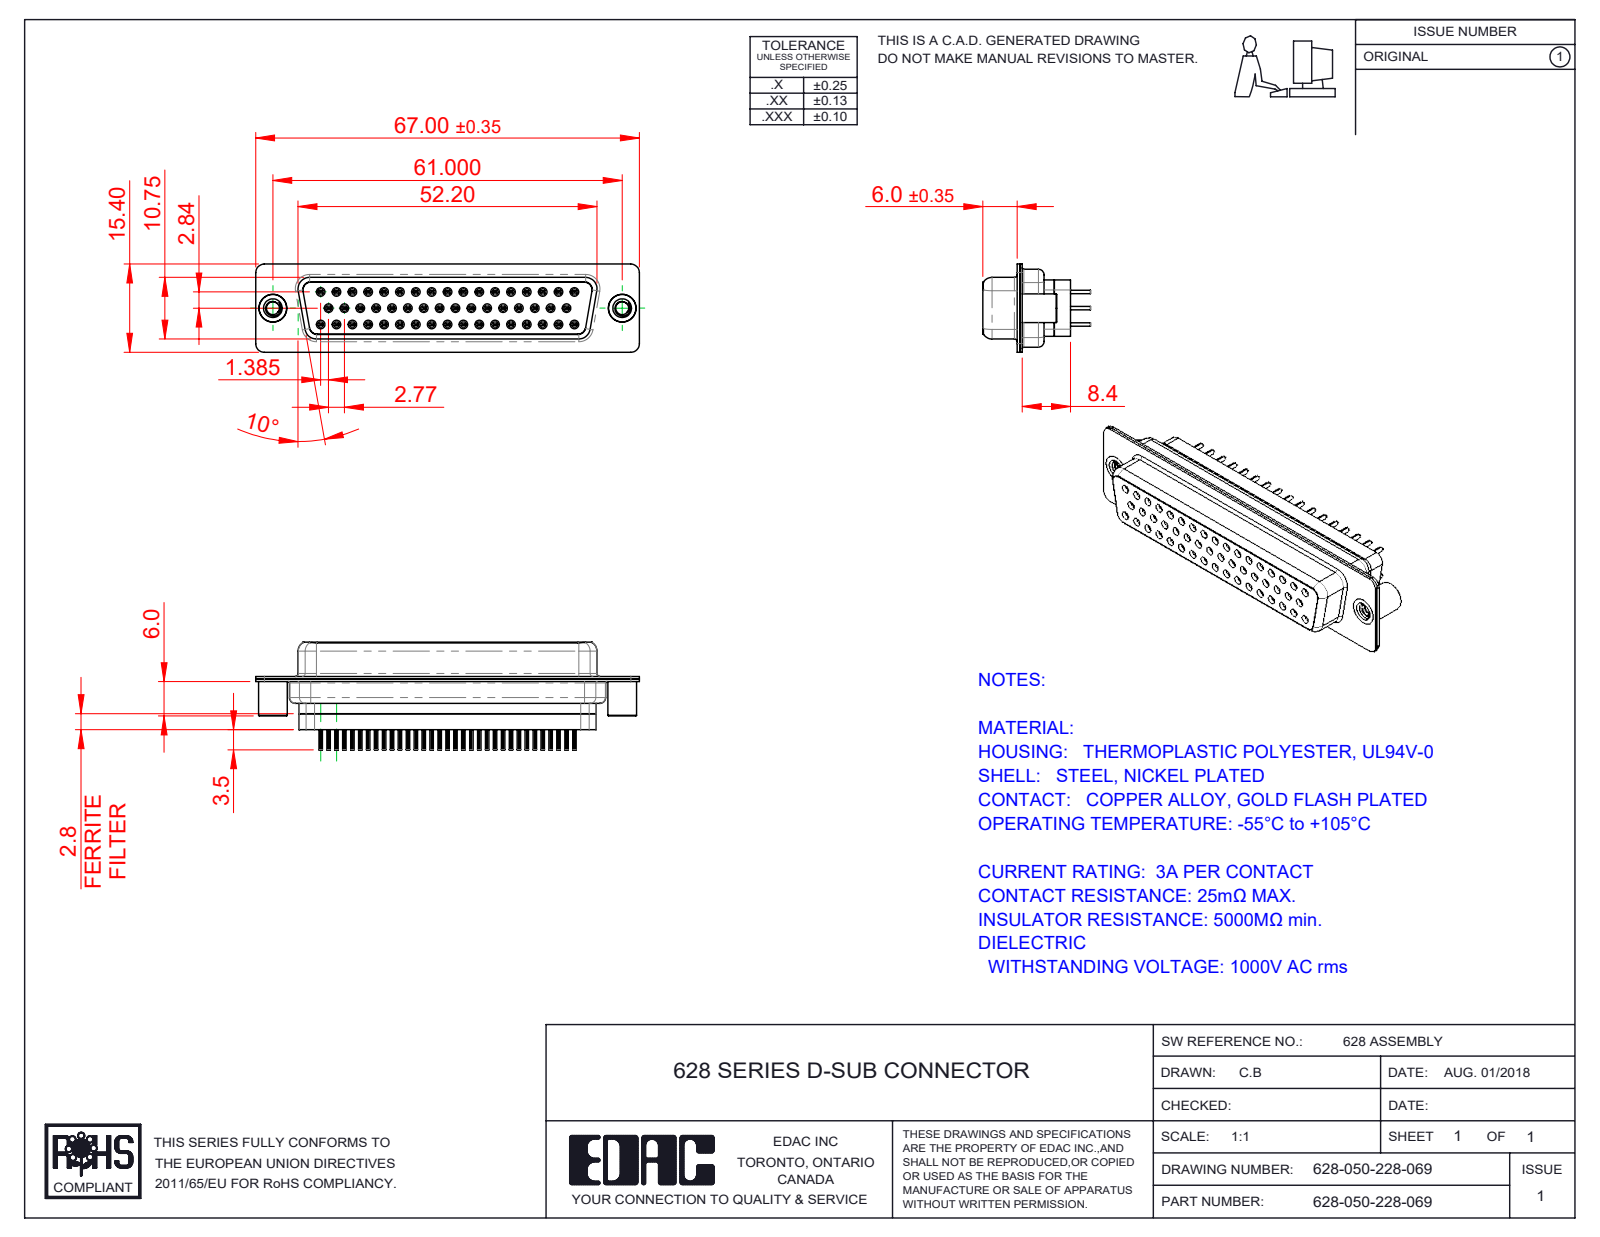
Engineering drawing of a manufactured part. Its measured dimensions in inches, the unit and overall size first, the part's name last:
Units: inches
Overall size (bounding box): 2.638 × 0.74 × 0.606
Round holes (diameter × count): ⌀0.008 ×50, ⌀0.031 ×50, ⌀0.035 ×50, ⌀0.043 ×50, ⌀0.063 ×50, ⌀0.067 ×17, ⌀0.089 ×2, ⌀0.157 ×2, ⌀0.159 ×2, ⌀0.191 ×2
Round bosses / shafts (diameter × count): ⌀0.079 ×50, ⌀0.059 ×50, ⌀0.047 ×50, ⌀0.024 ×50, ⌀0.197 ×2, ⌀0.195 ×2, ⌀0.189 ×2
Partial cylindrical surfaces — rounded edges, fillets, slot ends (radius × count): R0.004 ×100, R0.011 ×33, R0.059 ×16, R0.079 ×12, R0.053 ×8, R0.01 ×4, R0.02 ×4, R0.024 ×4
Main face-to-face distances: 0.018, 0.016, 0.238, 0.074, 0.446, 0.366, 0.388, 0.256, 0.035, 0.406
Hole centre spacings: 0.109, 0.124, 0.218, 0.327, 0.436, 0.545, 0.654, 0.763
Volume: 0.485 in³ · Surface area: 27.31 in²
Bodies: 56 solids, 6762 faces (1623 planar, 1912 cylindrical, 3227 other)
Part name (STEP PRODUCT): 628 Contact Row 2_28L; 628 Shell Front_50 Contacts; 628 Shell Rear_50 Contacts; 628 4-40 Threaded Standoff BS (+4 more)
STEP written by: SolidWorks 2020 (CONFIG_CONTROL_DESIGN)
